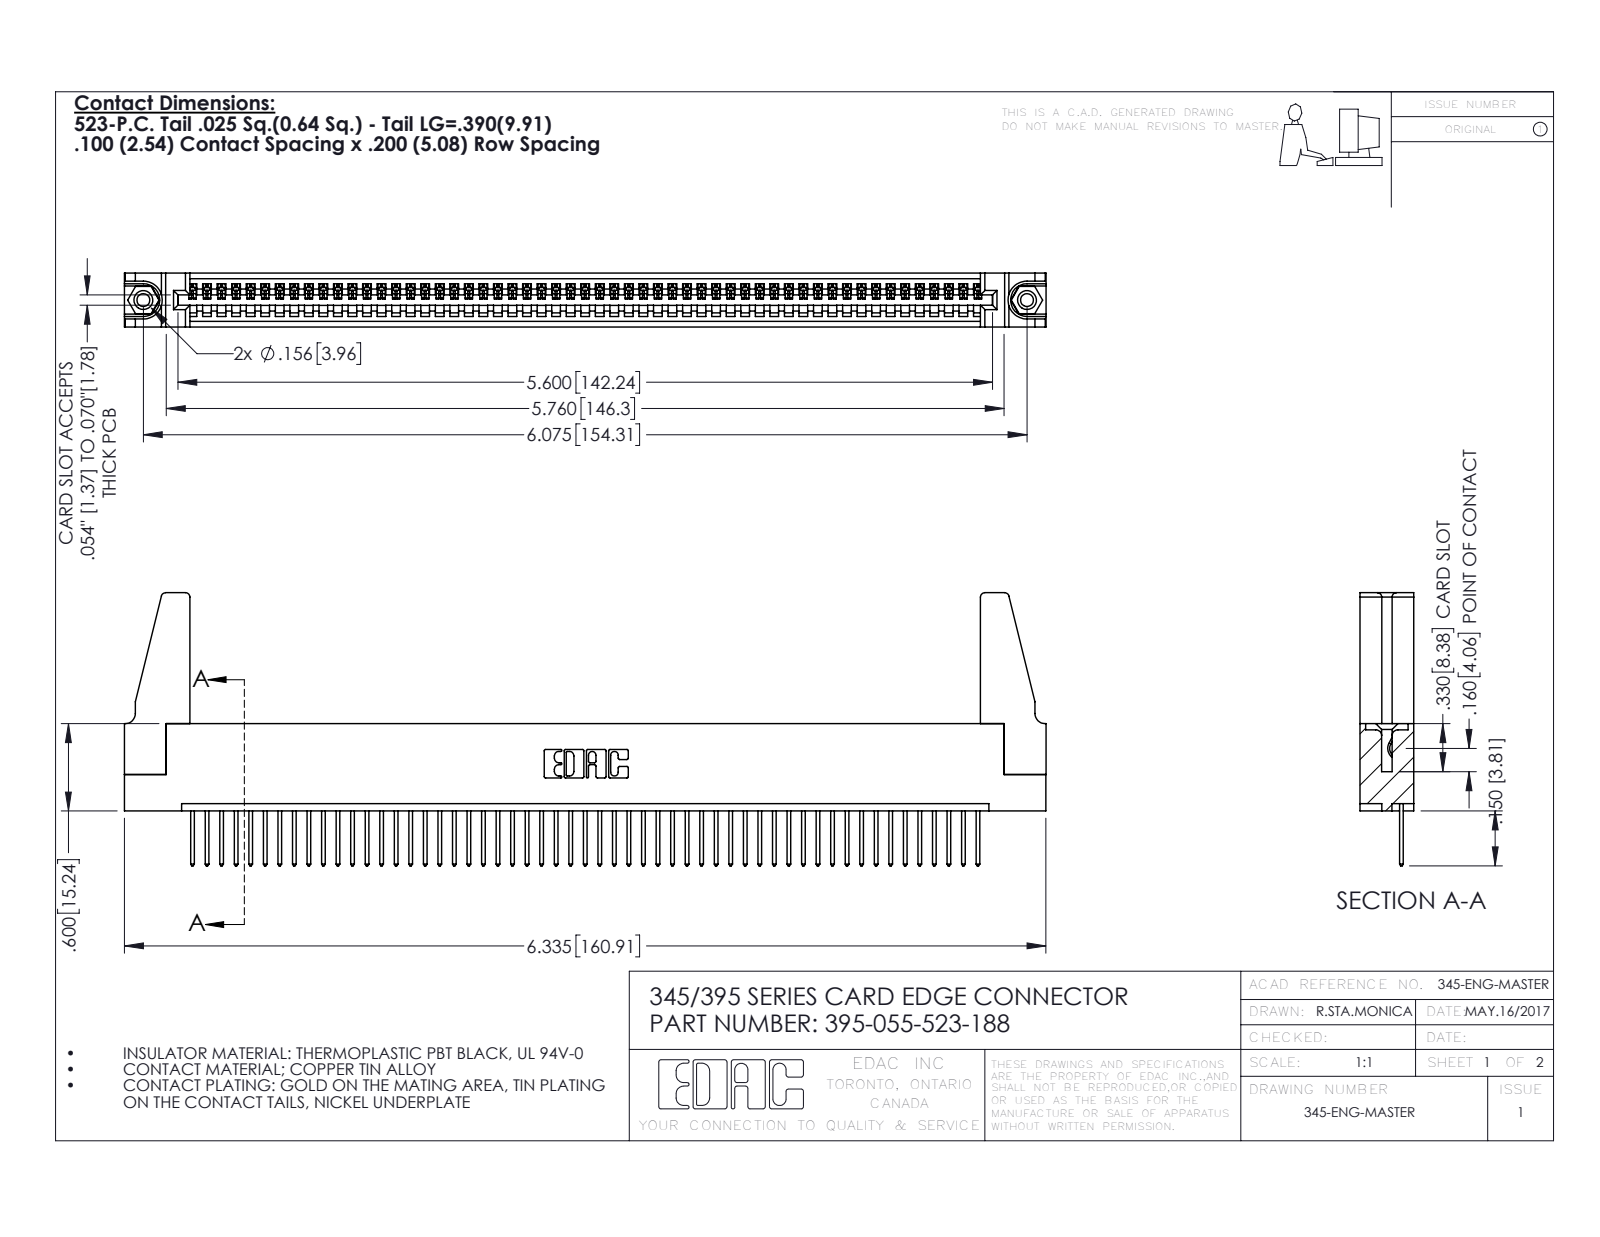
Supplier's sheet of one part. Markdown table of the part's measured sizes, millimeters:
| quantity | value |
| --- | --- |
| part name | 395-055-523-188; 345 Part_Flush Mounting Lugs - 0.156 Dia-TH; 345-220-078_345-220-088; 345-292-001_345-293-123 (+1 more) |
| STEP written by | SolidWorks 2016 (CONFIG_CONTROL_DESIGN) |
| units | millimeters |
| bodies | 60 solids, 3440 faces (2352 planar, 1072 cylindrical, 16 other) |
| overall size | 160.9 × 47.7 × 9.4 |
| volume | 18 620 mm³ |
| surface area | 23 790 mm² |
| round holes (diameter × count) | 2.3 × 2, 3.2 × 2, 4 × 2, 1.6 × 1 |
| round bosses / shafts (diameter × count) | 3.9 × 2 |
| partial cylindrical surfaces (radius × count) | 0.2 × 110, 0.3 × 110, 0.3 × 22, 0.8 × 8, 0.2 × 6, 0.8 × 6, 0.7 × 3, 0.8 × 2 |
| main face-to-face distances | 1.8, 7.6, 9.4, 5.1, 2.5, 6.9, 0.6, 5.7, 3.8, 1.8 |
| hole center spacings | 6.9, 148.3, 154.3 |
